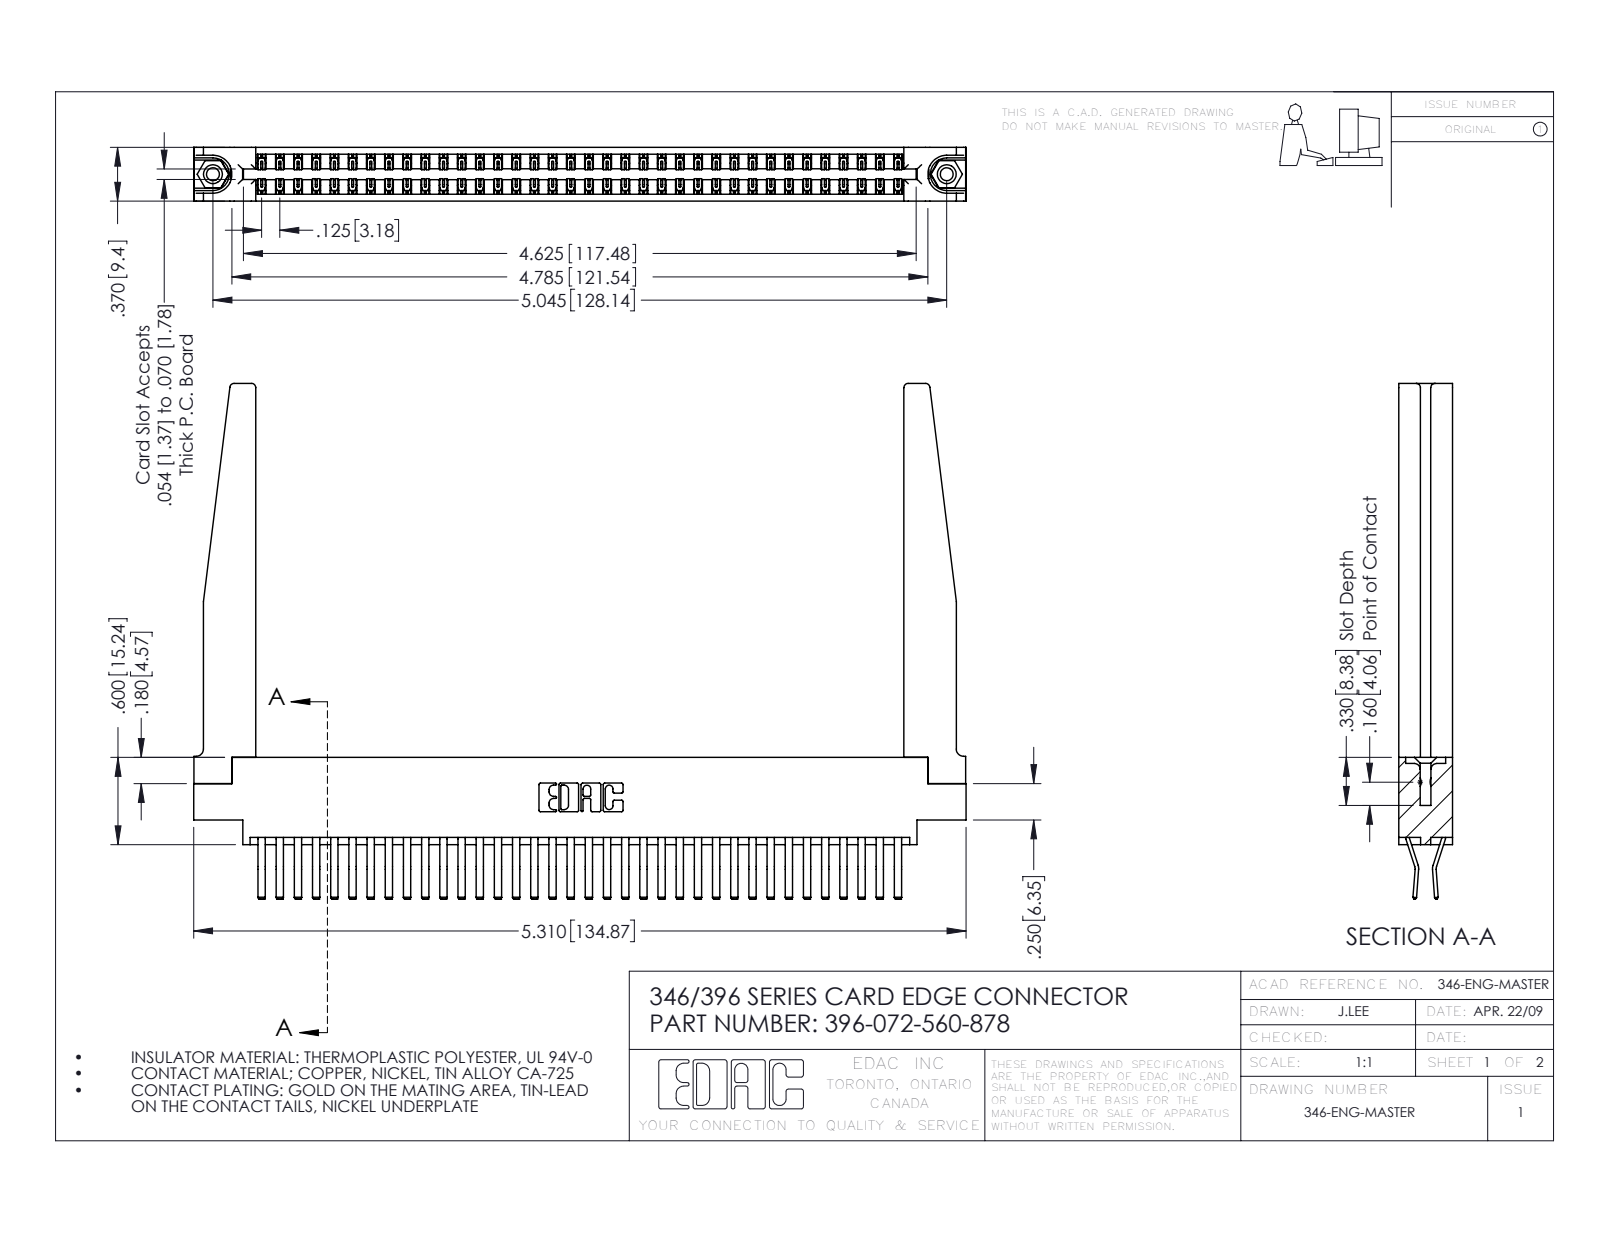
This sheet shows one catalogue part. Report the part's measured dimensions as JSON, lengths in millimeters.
{"part_name": "346-220-078_345-220-078; 396-072-560-878; 346 Part_0.170 Offset - 0.156 Dia-TH; 345-250-001_345-250-001-102 (+1 more)", "step_written_by": "SolidWorks 2016 (CONFIG_CONTROL_DESIGN)", "units": "millimeters", "bodies": {"solids": 77, "faces": 4248, "planar": 2742, "cylindrical": 1454, "other": 52}, "overall_size": [134.9, 90, 9.4], "volume_mm3": 20340, "surface_area_mm2": 26330, "round_holes": [[2.3, 2], [3.2, 2], [4, 2], [1.6, 1]], "round_bosses_or_shafts": [[3.9, 2]], "partial_cylinders_radius": [[0.2, 108], [0.3, 22], [0.8, 8], [0.2, 6], [0.8, 6], [1.3, 4], [0.7, 3], [0.3, 2]], "face_to_face_distances": [9.4, 1.2, 8.2, 1.8, 0.6, 3.8, 3.8, 6.4, 7.6, 7], "hole_center_spacings": [6.2, 122.8, 128.1]}
